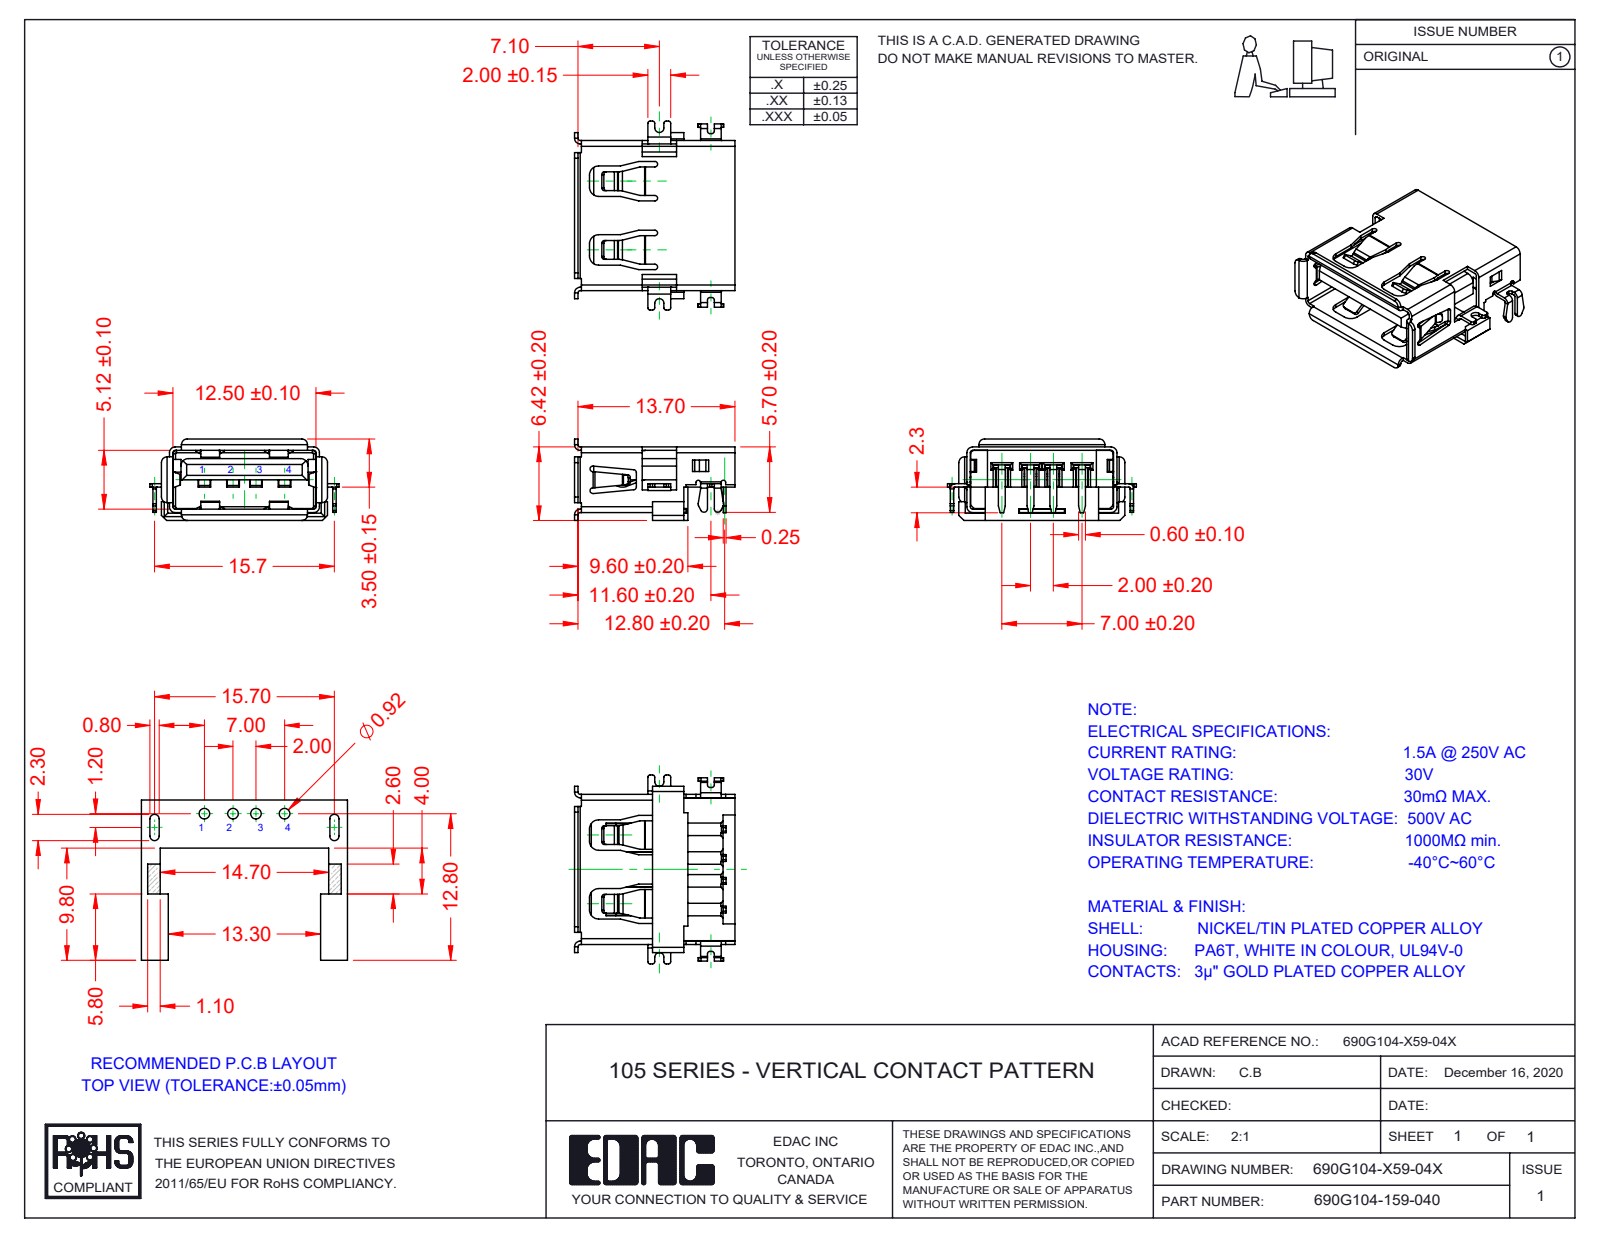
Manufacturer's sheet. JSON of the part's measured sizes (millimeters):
{"part_name": "Contacts 690G104-X59-04X; Shell 690G104-X59-04X; Insulator 690G104-X59-04X_White; 690G104-159-040", "step_written_by": "SolidWorks 2020 (AUTOMOTIVE_DESIGN)", "units": "millimeters", "bodies": {"solids": 6, "faces": 831, "planar": 604, "cylindrical": 201, "other": 26}, "overall_size": [16.5, 14, 7.12], "volume_mm3": 424, "surface_area_mm2": 1771, "partial_cylinders_radius": [[0.2, 34], [0.5, 24], [0.25, 21], [0.1, 12], [0.3, 8], [0.4, 7], [0.8, 6], [0.15, 3]], "face_to_face_distances": [5.42, 2.56, 2.86, 0.72, 4.7, 2.5, 1, 1.02, 5.12, 0.7]}
